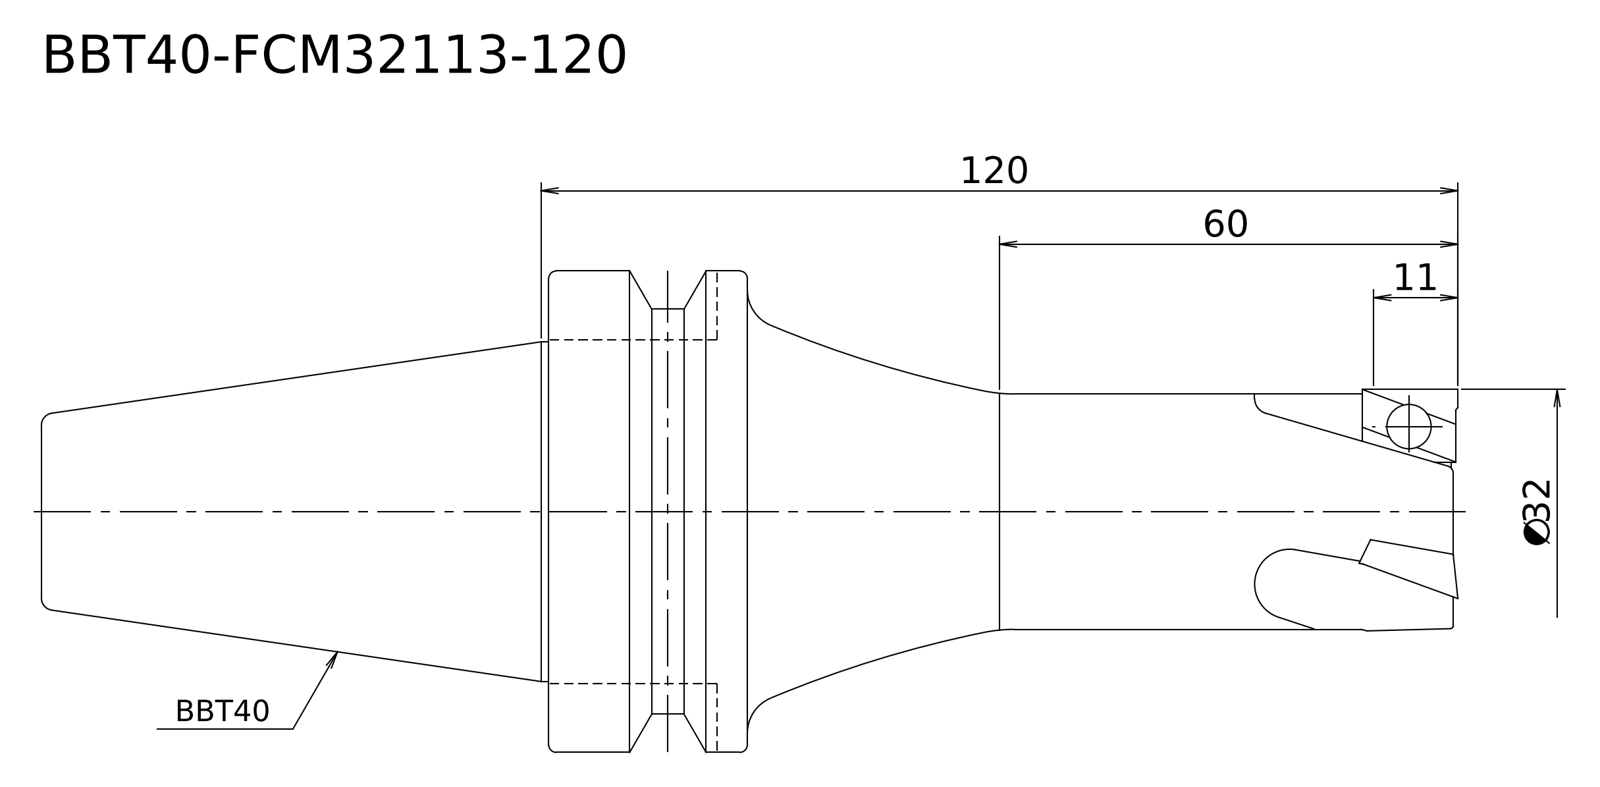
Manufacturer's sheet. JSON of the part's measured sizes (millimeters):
{"step_written_by": "Kubotek KeyCreator V8.5.1 (14335) (CONFIG_CONTROL_DESIGN)", "units": "millimeters", "bodies": {"solids": 1, "faces": 17, "planar": 4, "cylindrical": 6, "other": 7}, "overall_size": [185.4, 63, 63], "volume_mm3": 230016, "surface_area_mm2": 27392, "round_bosses_or_shafts": [[63, 1], [53, 1], [44.45, 1], [32, 1], [30.8, 1]], "face_to_face_distances": [119, 185.4, 66.4, 93, 26, 92.4]}
